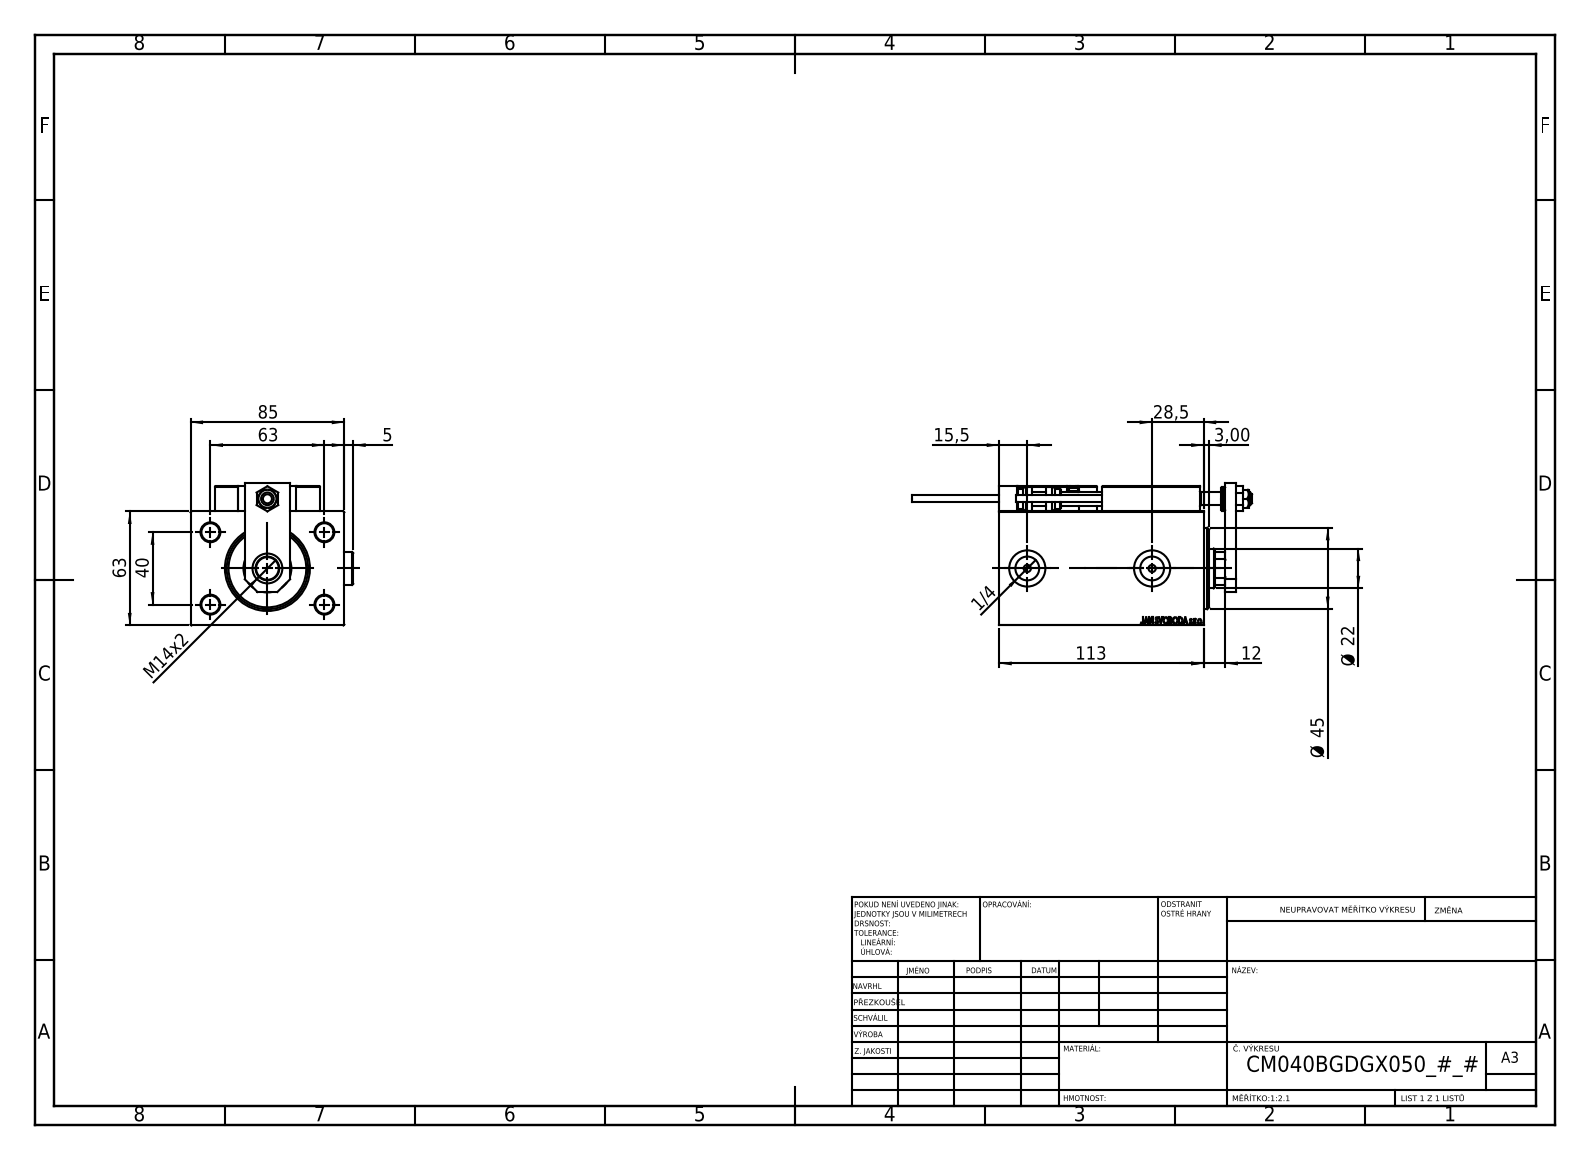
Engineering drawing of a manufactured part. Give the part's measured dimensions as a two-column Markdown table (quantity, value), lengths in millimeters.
| quantity | value |
| --- | --- |
| part name | MAGNET; NUT_D10; Block; V450CM_VC_B (+7 more) |
| STEP written by | SolidWorks 2019 (CONFIG_CONTROL_DESIGN) |
| units | millimeters |
| bodies | 26 solids, 1372 faces (595 planar, 200 cylindrical, 577 other) |
| overall size | 187.7 × 89.9 × 78.5 |
| volume | 597 621 mm³ |
| surface area | 110 419 mm² |
| round holes (diameter × count) | 4 × 6, 8 × 5, 3.2 × 4, 10 × 4, 5 × 2, 13.16 × 2, 20 × 2, 7 × 1, 12.5 × 1, 16.5 × 1, 22 × 1, 25.5 × 1 |
| round bosses / shafts (diameter × count) | 18 × 2, 5 × 2, 3.8 × 2, 13 × 1, 11 × 1 |
| partial cylindrical surfaces (radius × count) | 0.3 × 30, 3 × 2, 10.5 × 1 |
| main face-to-face distances | 63, 85, 12, 113, 101, 14, 77, 18, 3, 30 |
| hole center spacings | 37.31, 11.37, 20, 29.59, 29.69, 36.06, 36.53, 40 |
